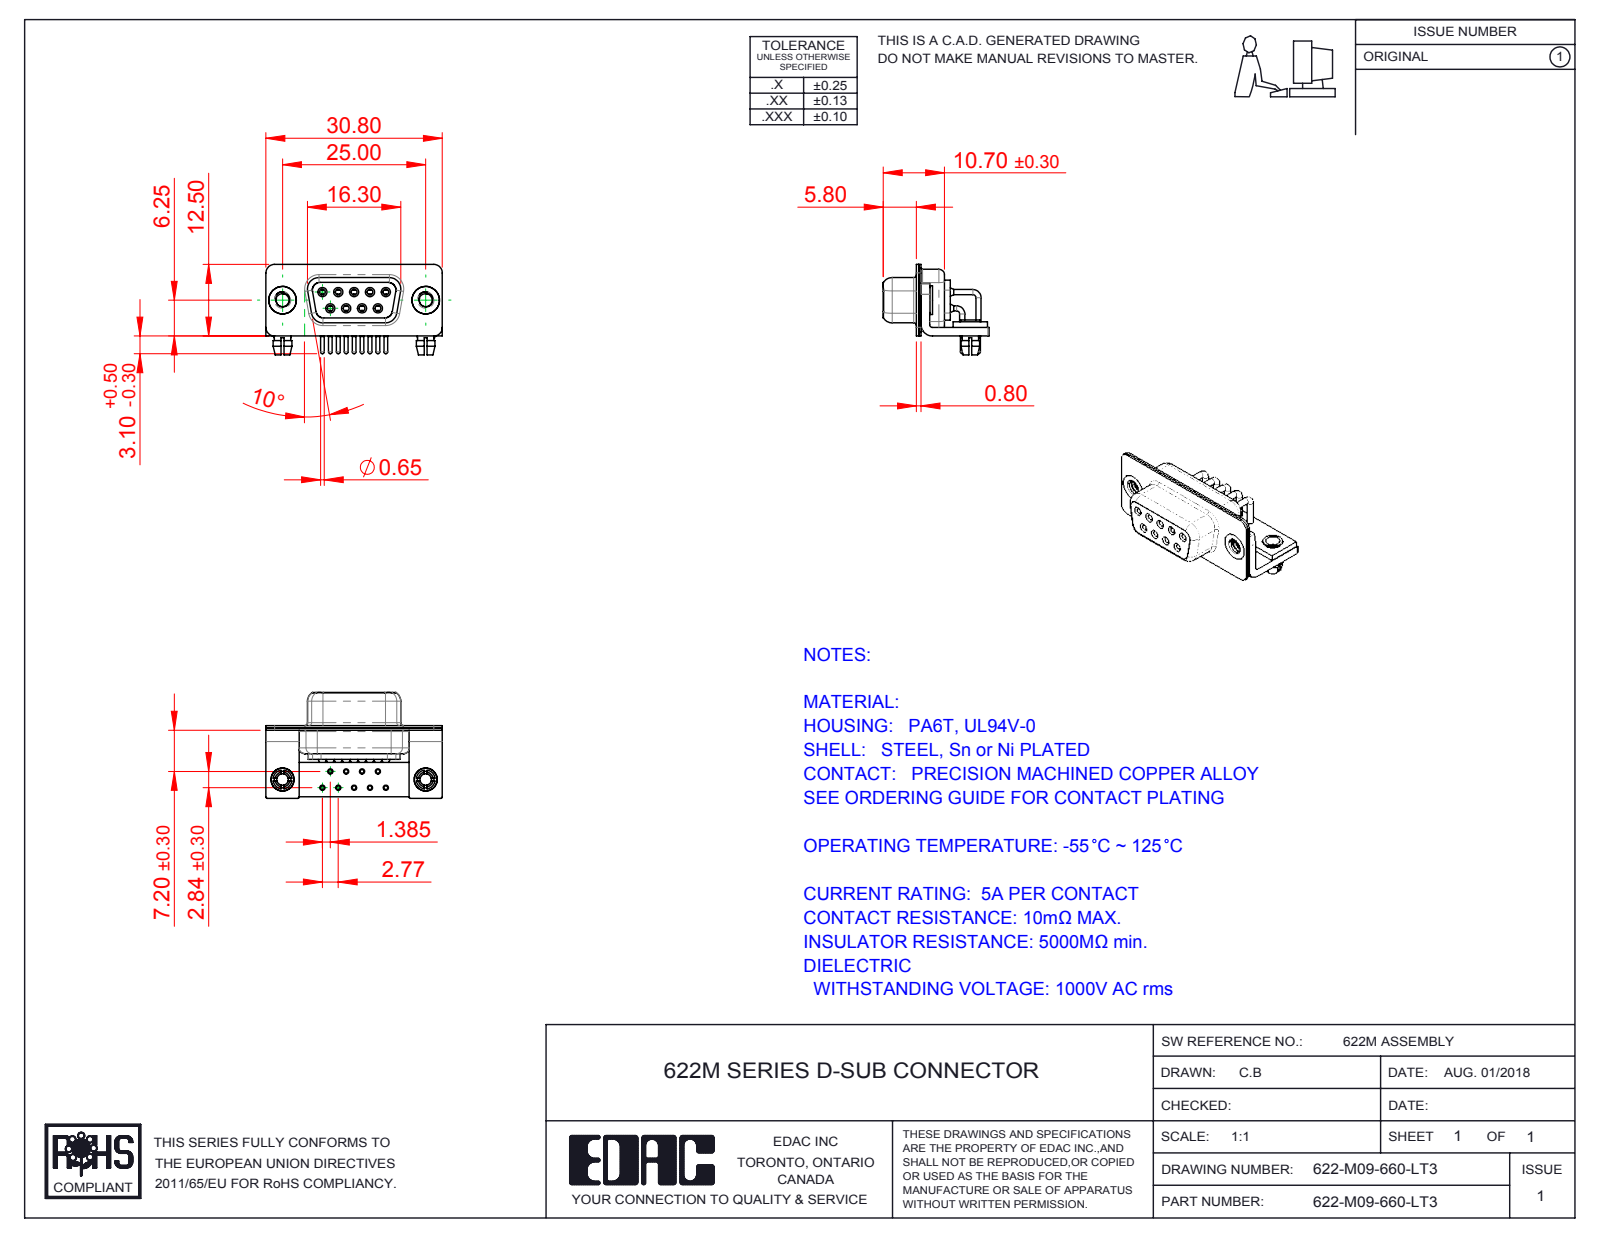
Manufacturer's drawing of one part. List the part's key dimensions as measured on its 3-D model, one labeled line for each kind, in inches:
Part name (STEP PRODUCT): 622M 4-40 Threaded Rivet_Stabilizer; 622M Contact Row 2; 622M Contact Row 1; 622M Shell Rear_09 Contacts (+6 more)
STEP written by: SolidWorks 2016 (CONFIG_CONTROL_DESIGN)
Units: inches
Bodies: 19 solids, 916 faces (276 planar, 416 cylindrical, 224 other)
Overall size (bounding box): 1.213 × 0.728 × 0.622
Volume: 0.133 in³ · Surface area: 8.933 in²
Round holes (diameter × count): ⌀0.079 ×11, ⌀0.035 ×9, ⌀0.039 ×9, ⌀0.043 ×9, ⌀0.067 ×9, ⌀0.071 ×9, ⌀0.089 ×2, ⌀0.098 ×2, ⌀0.126 ×2, ⌀0.157 ×2, ⌀0.189 ×2
Round bosses / shafts (diameter × count): ⌀0.063 ×9, ⌀0.059 ×9, ⌀0.035 ×9, ⌀0.026 ×9, ⌀0.197 ×2, ⌀0.193 ×2, ⌀0.157 ×2, ⌀0.134 ×2
Partial cylindrical surfaces — rounded edges, fillets, slot ends (radius × count): R0.01 ×16, R0.059 ×16, R0.079 ×13, R0.053 ×8, R0.063 ×8, R0.02 ×5, R0.024 ×4, R0.026 ×4
Main face-to-face distances: 0.016, 0.031, 0.059, 0.091, 0.075, 0.039, 0.368, 0.057, 0.352, 0.033
Hole centre spacings: 0.124, 0.109, 0.218, 0.198, 0.198, 0.327, 0.294, 0.295
